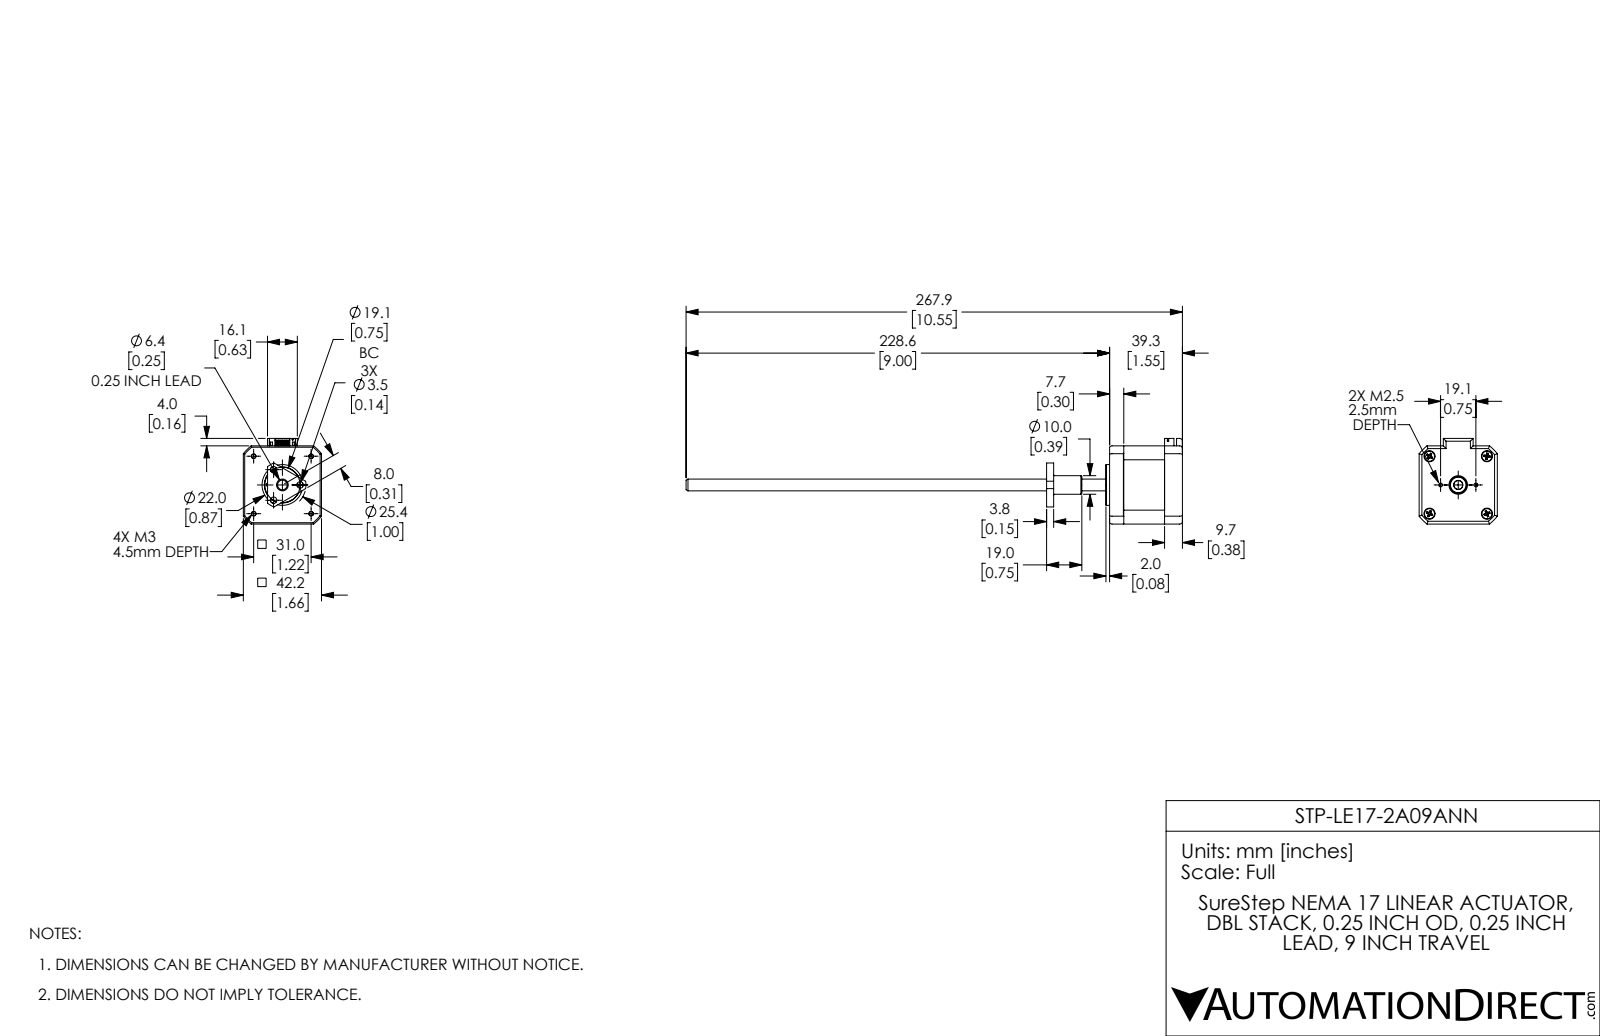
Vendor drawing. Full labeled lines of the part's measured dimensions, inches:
Part name (STEP PRODUCT): STP-LE17-2A09ANN; STP-LE17-2A09ANN_2; STP-LE17-2A09ANN_1
STEP written by: SolidWorks 2017 (AUTOMOTIVE_DESIGN)
Units: inches
Bodies: 6 solids, 726 faces (360 planar, 232 cylindrical, 134 other)
Overall size (bounding box): 10.547 × 1.819 × 1.661
Volume: 4.049 in³ · Surface area: 46.01 in²
Round holes (diameter × count): ⌀0.098 ×4, ⌀0.15 ×4, ⌀0.236 ×4, ⌀0.138 ×3, ⌀0.059 ×2, ⌀0.081 ×2, ⌀0.193 ×1, ⌀0.197 ×1, ⌀0.512 ×1, ⌀0.669 ×1, ⌀0.766 ×1, ⌀0.787 ×1
Round bosses / shafts (diameter × count): ⌀0.213 ×4, ⌀0.115 ×4, ⌀1.063 ×1, ⌀1.02 ×1, ⌀0.866 ×1, ⌀0.472 ×1, ⌀0.394 ×1, ⌀0.354 ×1
Partial cylindrical surfaces — rounded edges, fillets, slot ends (radius × count): R0.039 ×12, R0.059 ×11, R0.098 ×2, R0.028 ×1, R0.5 ×1, R0.561 ×1, R0.63 ×1, R0.988 ×1
Main face-to-face distances: 1.661, 0.38, 1.547, 1.167, 1.246, 0.063, 0.866, 0.301, 0.039, 1.449
Hole centre spacings: 0.654, 0.375, 0.863, 1.159, 1.22, 0.194, 0.315, 0.51
